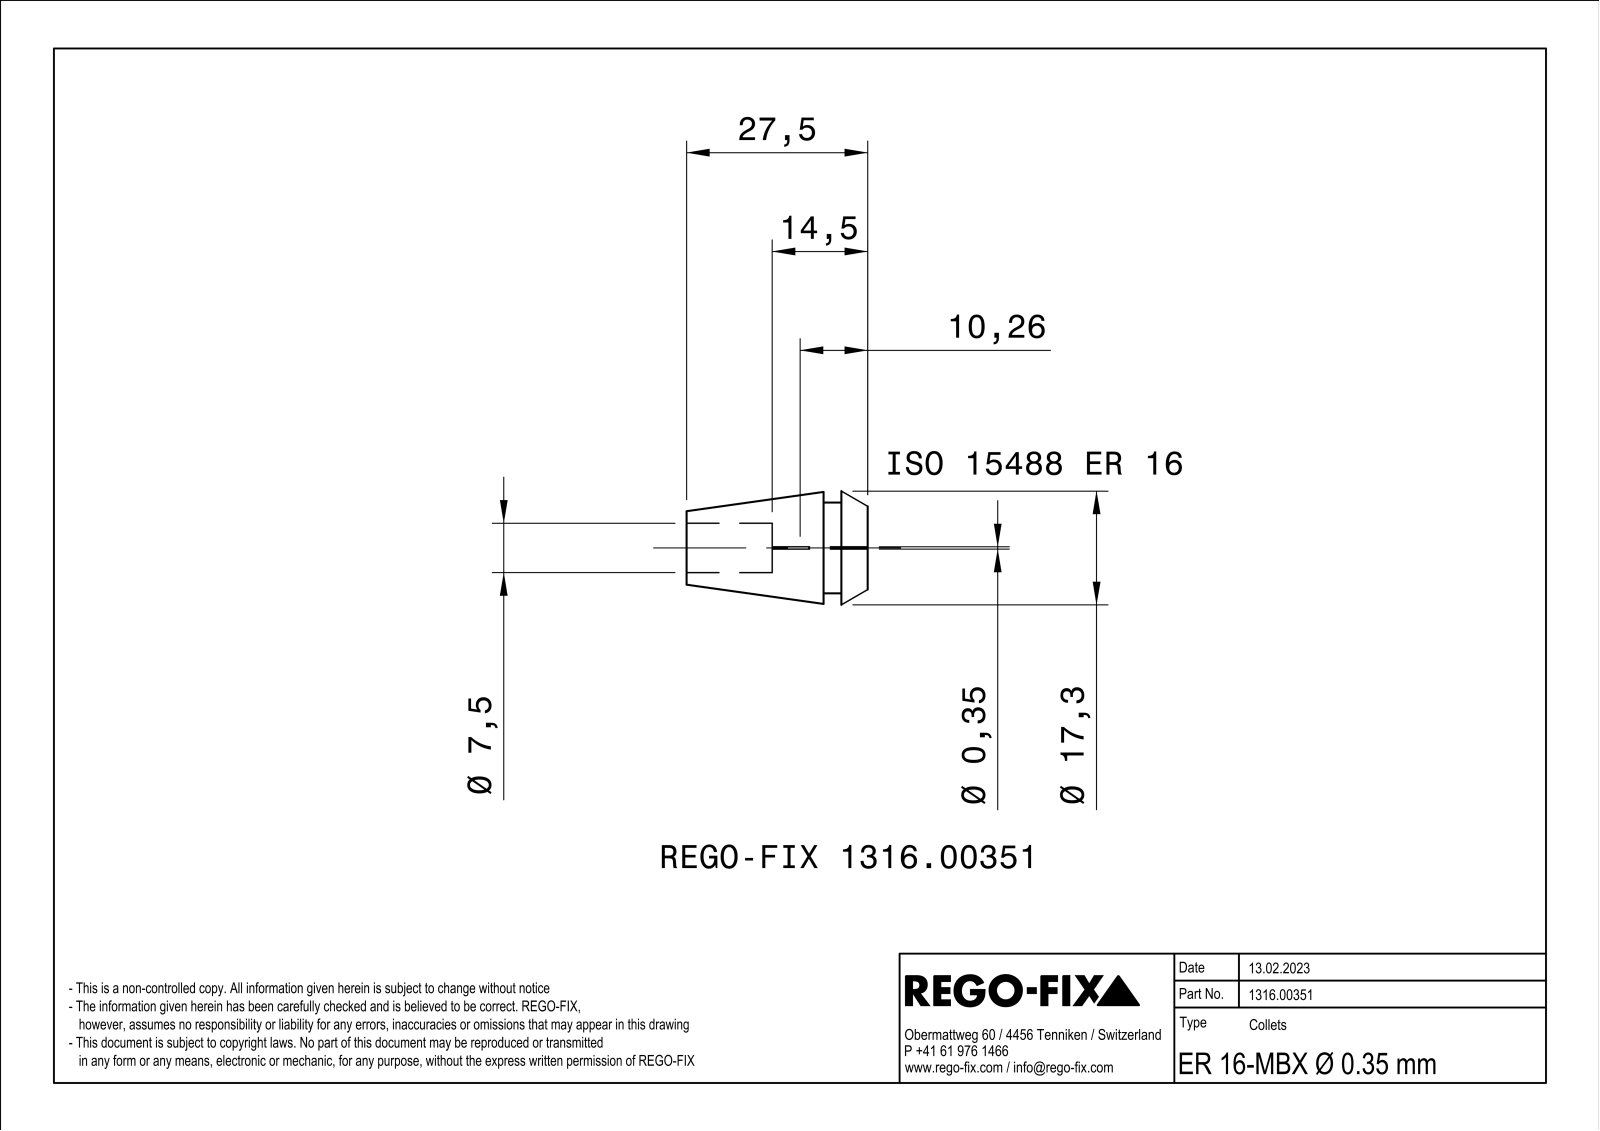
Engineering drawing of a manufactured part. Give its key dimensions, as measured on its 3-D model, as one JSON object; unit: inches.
{"part_name": "NOCUT", "step_written_by": "SIEMENS PLM Software Solid Edge ST10 (AUTOMOTIVE_DESIGN)", "units": "inches", "bodies": {"solids": 1, "faces": 109, "planar": 36, "cylindrical": 27, "other": 46}, "overall_size": [1.083, 0.666, 0.665], "volume_in3": 0.204, "surface_area_in2": 5.179, "round_holes": [[0.079, 3], [0.295, 1]], "round_bosses_or_shafts": [[0.543, 1]], "partial_cylinders_radius": [[0.984, 3], [0.007, 1]], "face_to_face_distances": [0.013, 0.018, 0.031, 0.264, 0.157, 0.106, 1.083, 0.925, 0.819, 0.571], "hole_center_spacings": [0.083, 0.143]}
